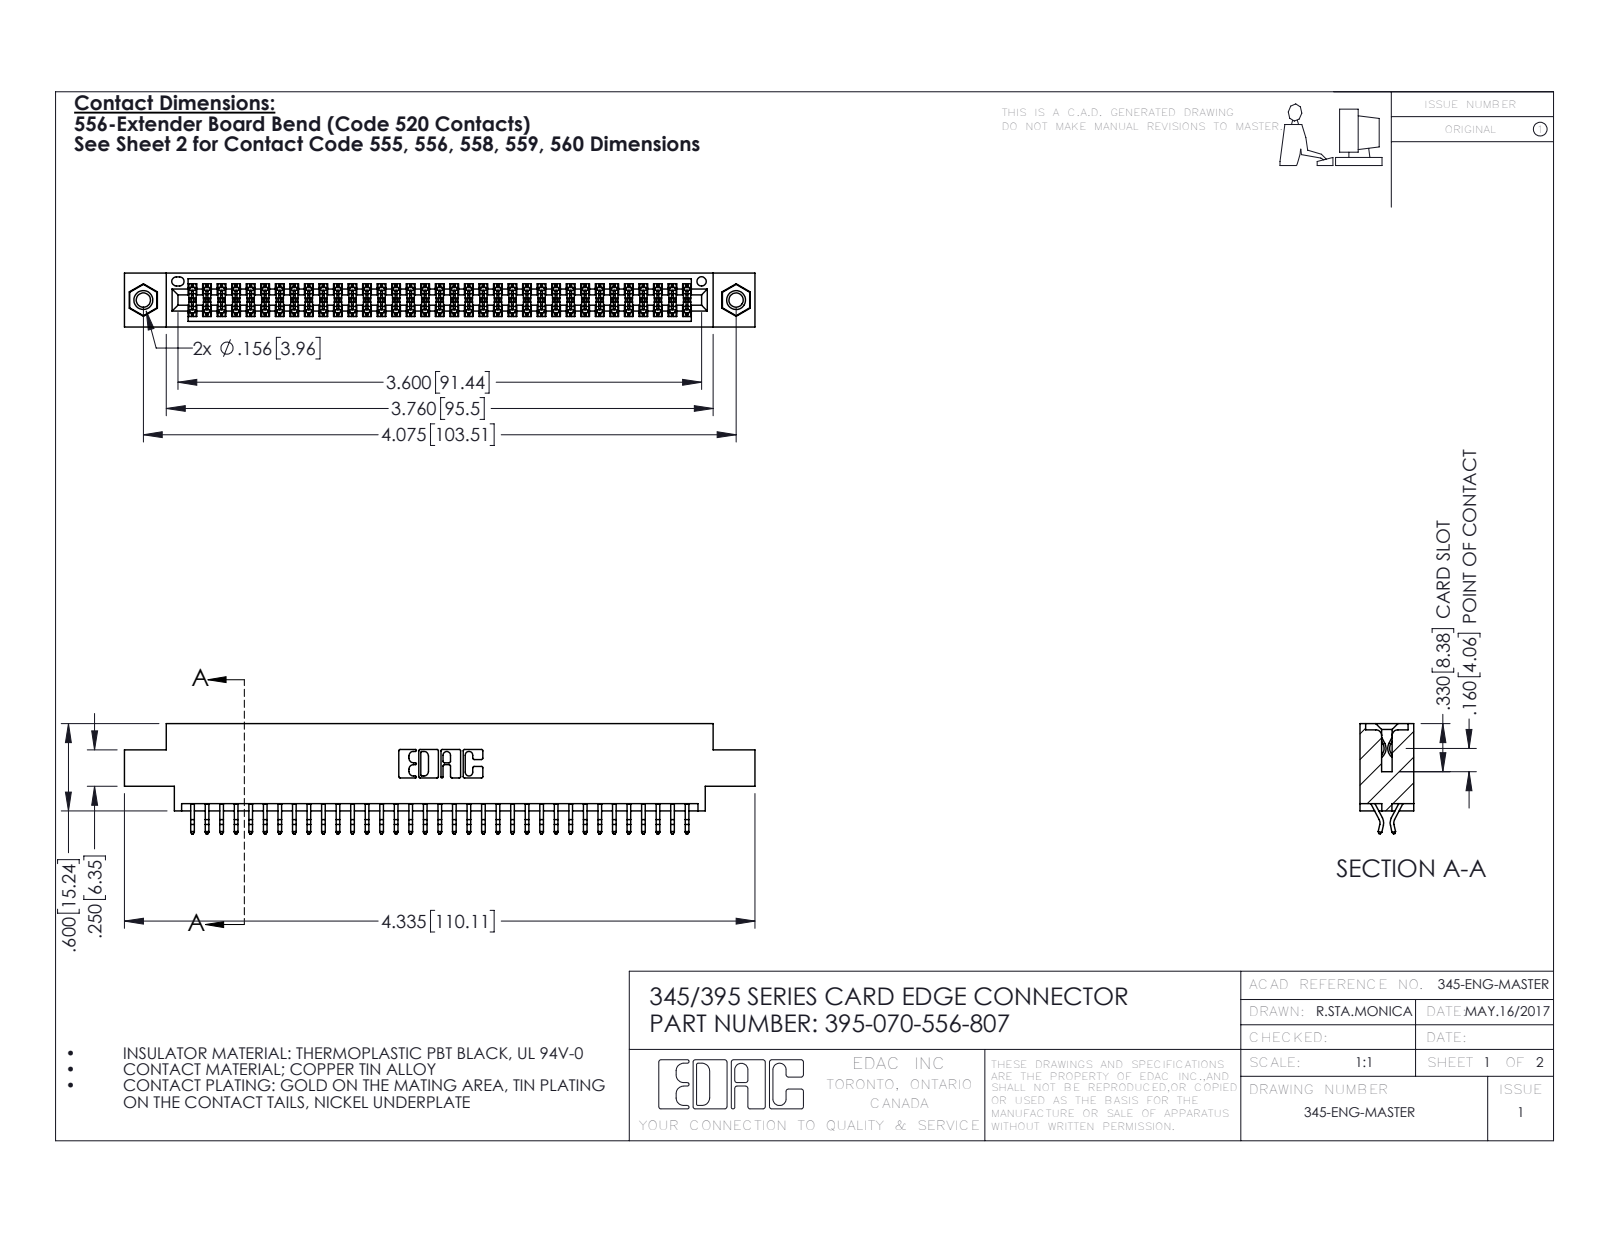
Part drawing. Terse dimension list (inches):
name: 345-292-001_556 Tail; 345-250-001_345-250-005-103; 345 Part_0.170 Offset - 0.156 Dia-TI; 395-070-556-807
written by: SolidWorks 2016 (CONFIG_CONTROL_DESIGN)
unit: in
bodies: 73 solids, 4110 faces (2706 planar, 1388 cylindrical, 16 other)
size: 4.335 × 0.757 × 0.37
volume: 0.641 in³; area: 24.02 in²
holes: 2× ⌀0.098, 2× ⌀0.125, 2× ⌀0.156, 1× ⌀0.064
bosses: 2× ⌀0.155
rounds: 105× R0.006, 22× R0.01, 6× R0.007, 6× R0.031, 3× R0.026, 2× R0.01, 2× R0.014, 2× R0.019
face distances: 0.072, 0.298, 0.37, 0.2, 0.025, 0.098, 0.272, 0.225, 0.175, 0.149
hole spacings: 0.27, 3.839, 4.075
